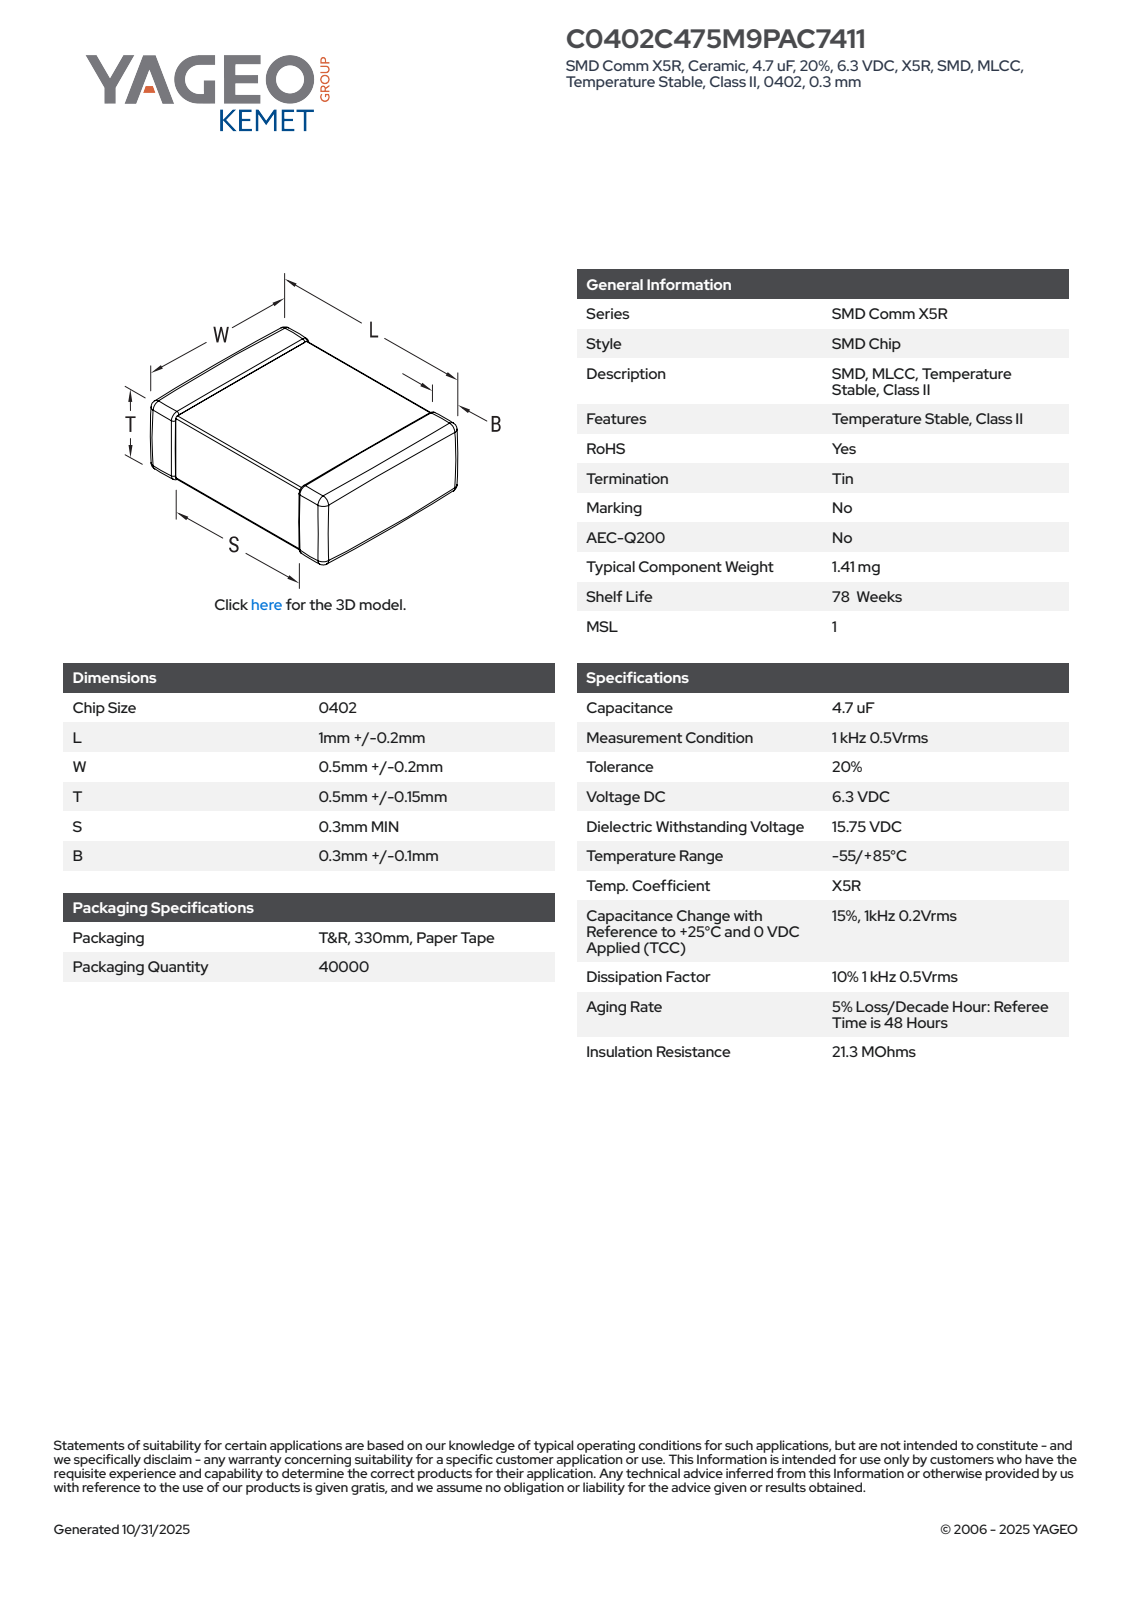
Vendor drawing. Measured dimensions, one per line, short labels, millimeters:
name: CCS_CCSTD_0402_L1.2W0.7T0.65B0.3
written by: SolidWorks 2021 (AUTOMOTIVE_DESIGN)
unit: mm
bodies: 4 solids, 125 faces (71 planar, 38 cylindrical, 16 other)
size: 1.2 × 0.7 × 0.65
volume: 0.53 mm³; area: 4 mm²
face distances: 0.64, 0.65, 0.69, 0.7, 1.2, 0.63, 0.68, 0.55, 0.6, 0.42
